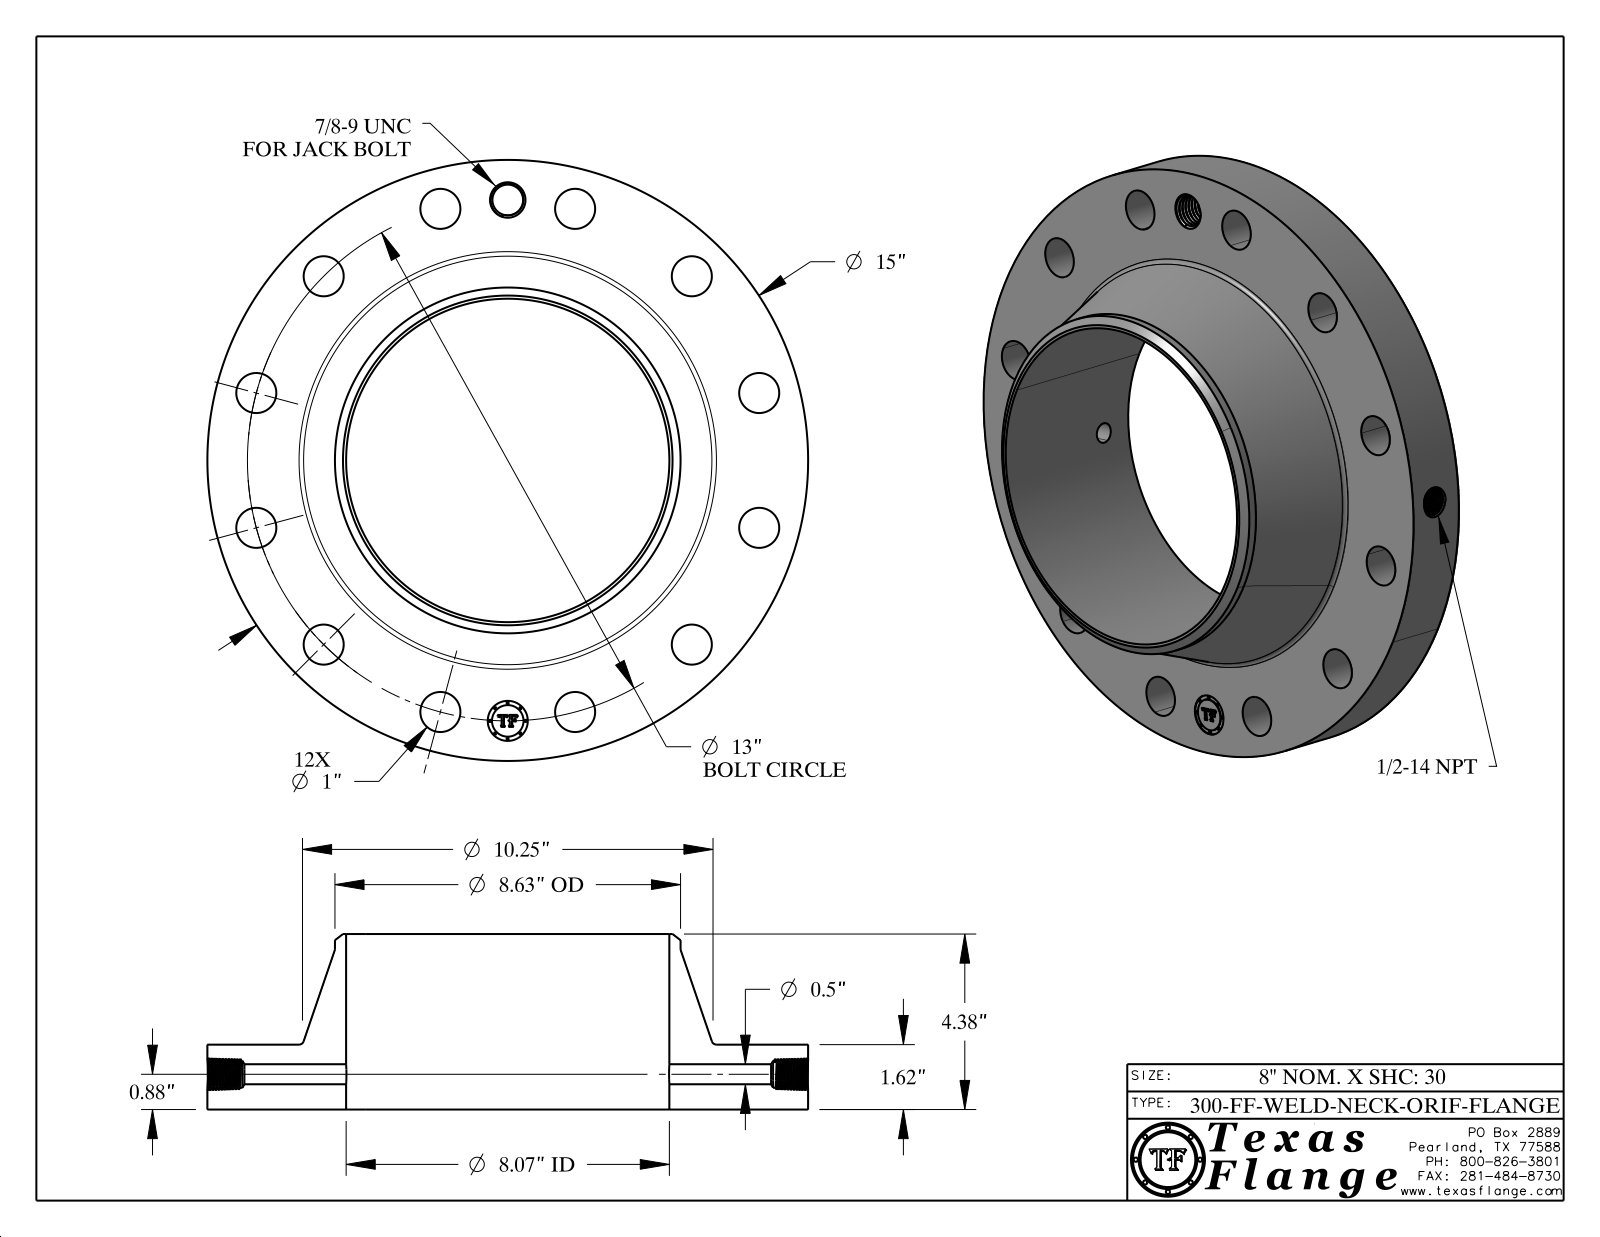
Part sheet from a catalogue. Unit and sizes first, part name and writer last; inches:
Units: inches
Overall size (bounding box): 15 × 15 × 4.38
Round holes (diameter × count): ⌀1 ×13, ⌀0.5 ×1, ⌀0.672 ×1, ⌀0.766 ×1, ⌀8.071 ×1
Round bosses / shafts (diameter × count): ⌀0.061 ×8, ⌀15 ×1, ⌀8.63 ×1, ⌀0.788 ×1
Main face-to-face distances: 1.62, 4.38, 2.76, 1.605, 0.015, 2.775, 0.298, 0.293, 0.054, 0.248
Hole centre spacings: 6.5, 3.365, 9.192, 11.258, 12.557, 13, 1.697, 4.975
Volume: 233 in³ · Surface area: 557.2 in²
Bodies: 1 solid, 770 faces (368 planar, 98 cylindrical, 304 other)
Part name (STEP PRODUCT): 300-FF-WELD-NECK
STEP written by: CATIA V5 STEP AP214 (AUTOMOTIVE_DESIGN)
